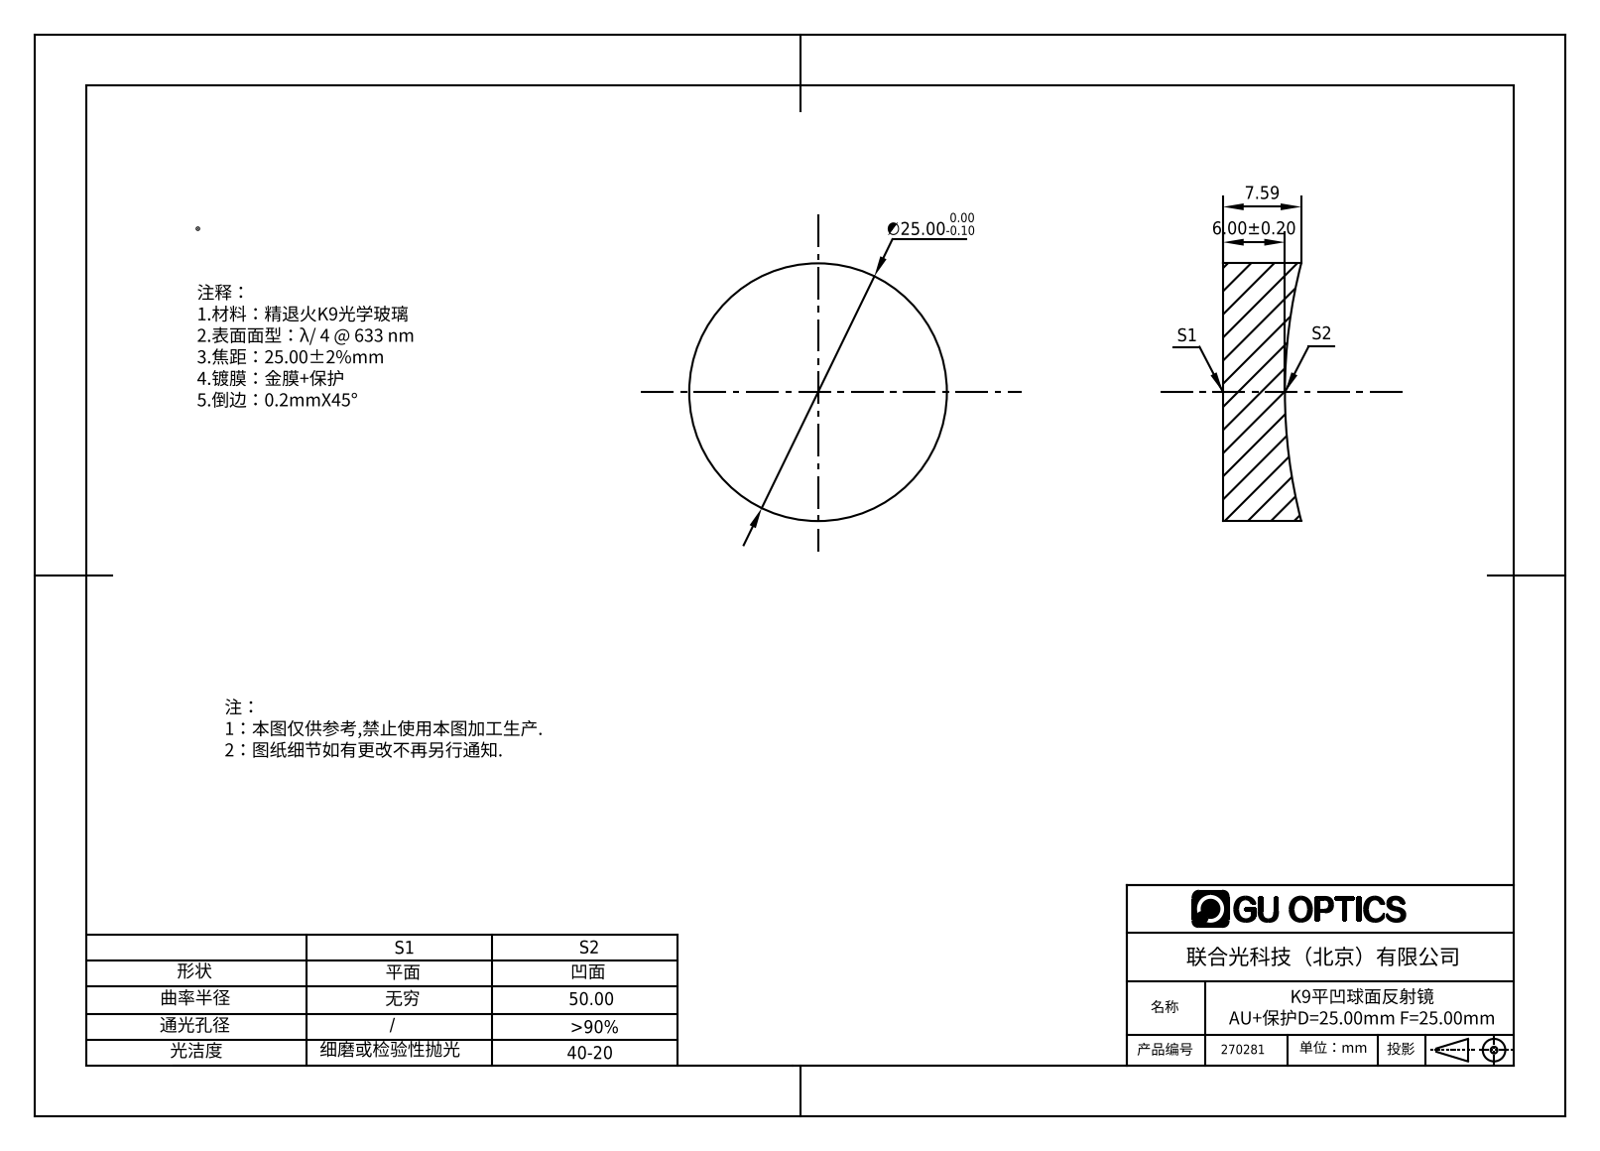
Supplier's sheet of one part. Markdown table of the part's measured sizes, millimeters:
| quantity | value |
| --- | --- |
| part name | 270021 |
| STEP written by | SolidWorks 2016 (AUTOMOTIVE_DESIGN) |
| units | millimeters |
| bodies | 1 solid, 5 faces (1 planar, 2 cylindrical, 2 other) |
| overall size | 25 × 25 × 7.59 |
| volume | 3 333 mm³ |
| surface area | 1 586 mm² |
| round bosses / shafts (diameter × count) | 25 × 1 |
